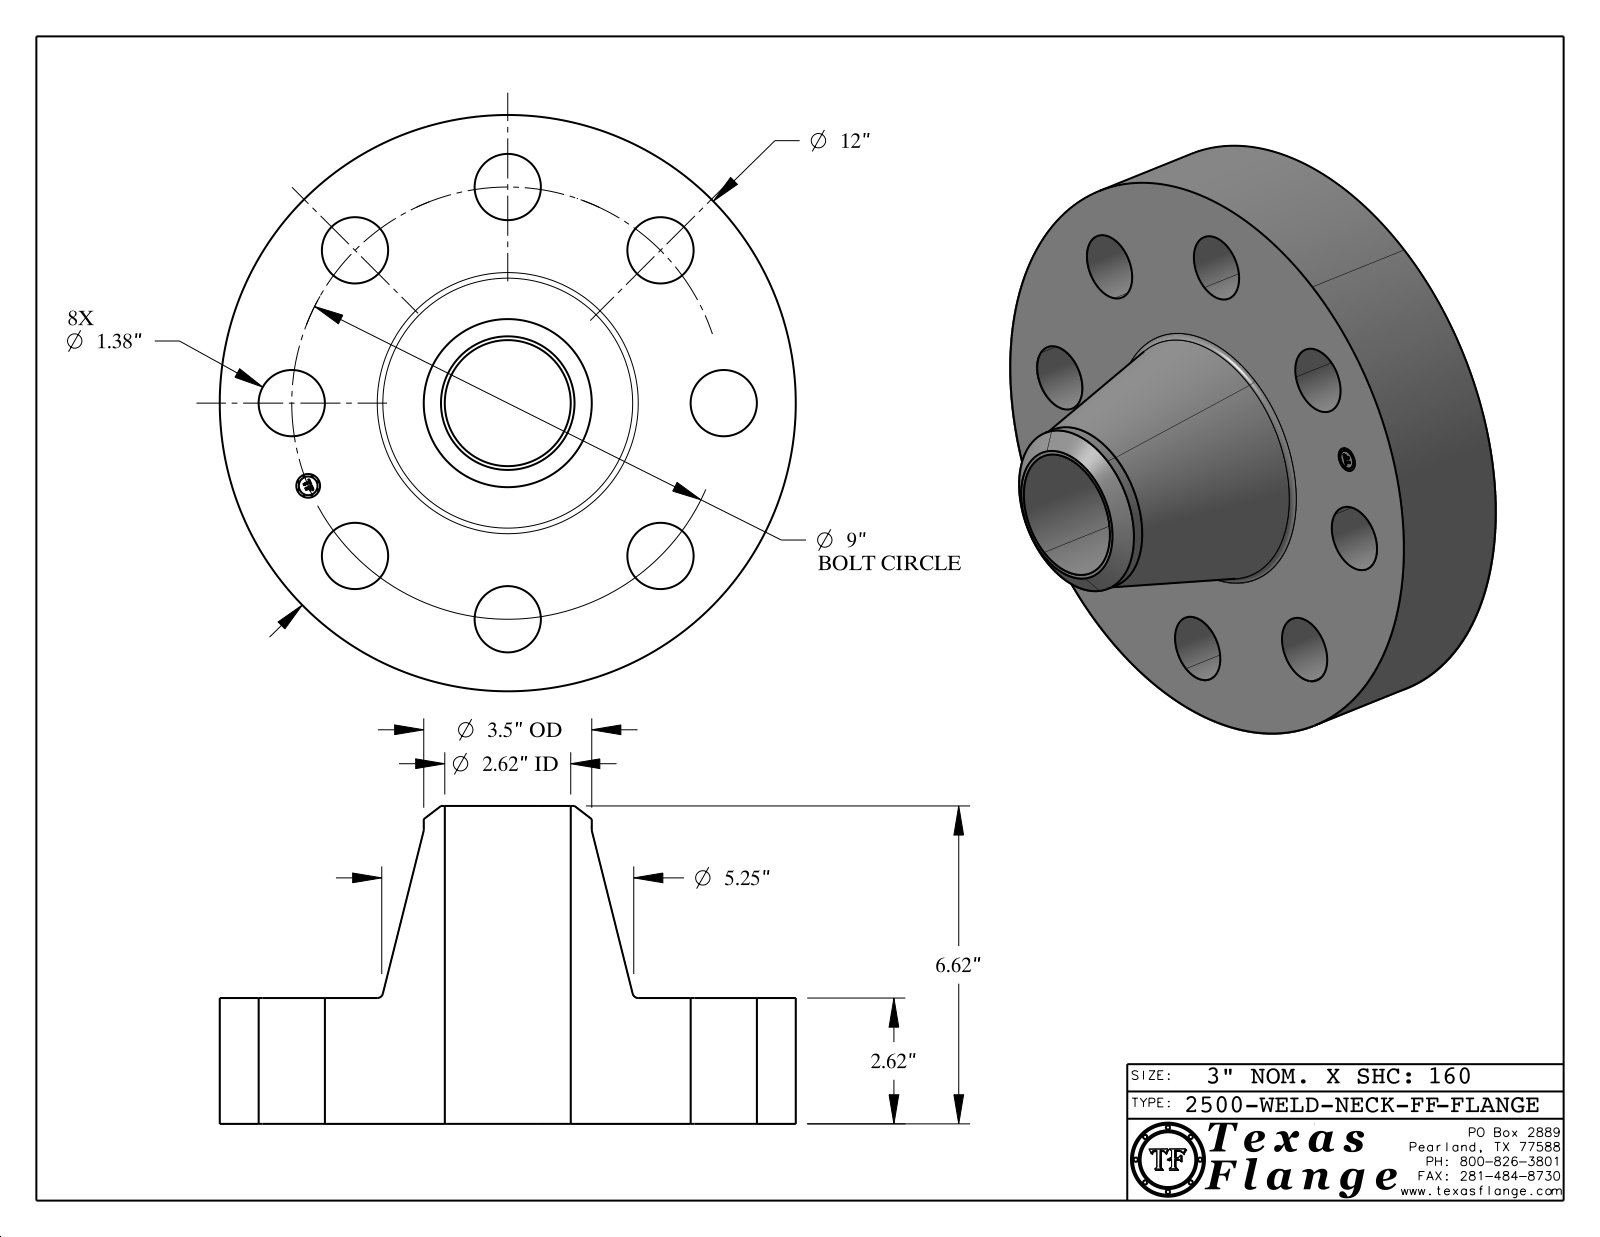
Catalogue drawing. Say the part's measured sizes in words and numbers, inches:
The part is named "2500-WELD-NECK-FF". Its 3-D file was written by "CATIA V5 STEP AP214 (AUTOMOTIVE_DESIGN)". It is 1 solid with 416 faces: 368 planar, 42 cylindrical and 6 other. Overall it measures 12 by 12 by 6.62 inches. Its volume is 286.7 cubic inches and its surface area 476.2 square inches. Round holes: 8 of diameter 1.38, 1 of diameter 0.495, 1 of diameter 2.624. Round bosses or shafts: 8 of diameter 0.03, 1 of diameter 12, 1 of diameter 3.5, 1 of diameter 0.39. The main face-to-face distances are 2.62, 6.62, 4, 2.605, 0.015, 4.015, 0.148, 0.144, 0.027, 0.096. The hole center spacings are 4.5, 3.444, 6.364, 8.315, 1.756, 5, 7.483, 9.
